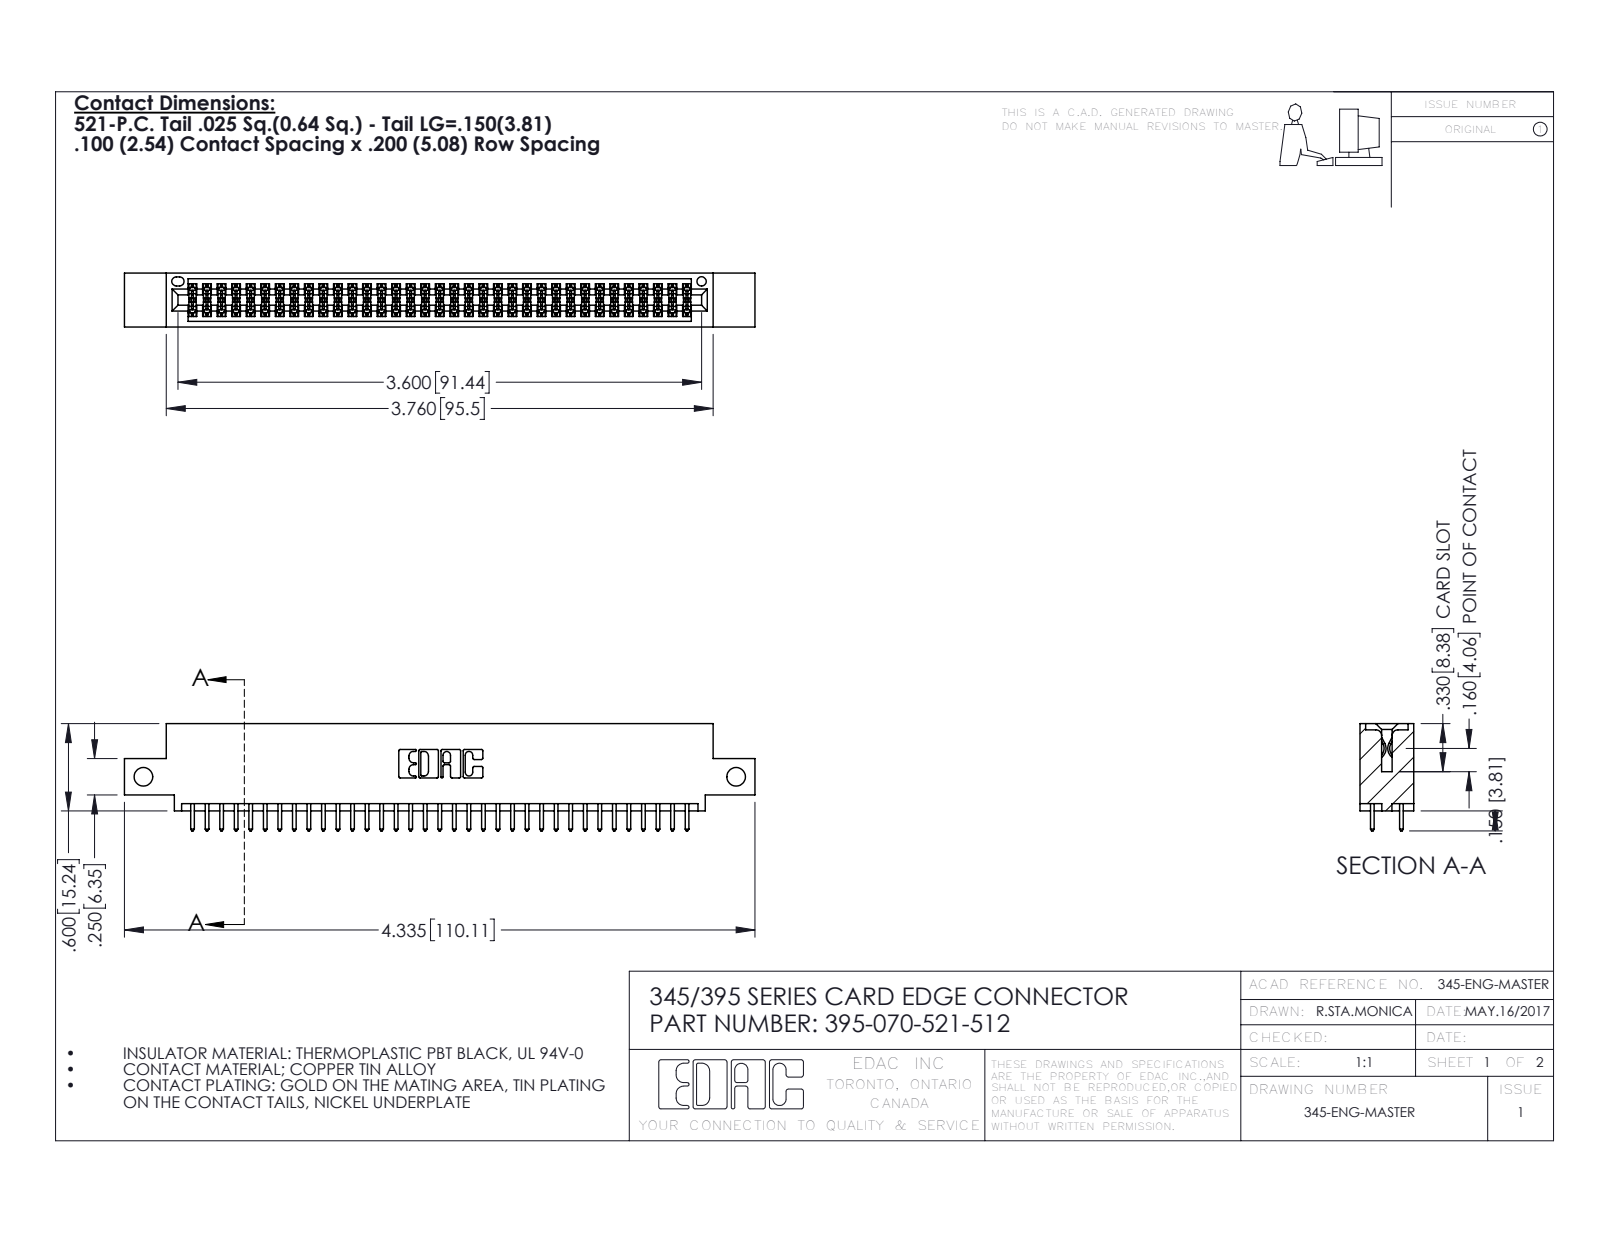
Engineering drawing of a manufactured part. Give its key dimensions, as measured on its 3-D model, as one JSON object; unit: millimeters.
{"part_name": "345 Part_0.110 Offset - Side Mount; 345-292-001_345-293-121; 395-070-521-512", "step_written_by": "SolidWorks 2016 (CONFIG_CONTROL_DESIGN)", "units": "millimeters", "bodies": {"solids": 71, "faces": 3630, "planar": 2394, "cylindrical": 1236, "other": 0}, "overall_size": [110.1, 18.7, 9.4], "volume_mm3": 10400, "surface_area_mm2": 15070, "round_holes": [[3.3, 2], [1.6, 1]], "partial_cylinders_radius": [[0.2, 105], [0.3, 70], [0.3, 22], [0.2, 6], [0.8, 6], [0.7, 3], [0.4, 2], [0.5, 2]], "face_to_face_distances": [7.6, 1.8, 5.1, 9.4, 2.5, 6.9, 0.6, 5.7, 4.4, 3.8], "hole_center_spacings": [103.5]}
